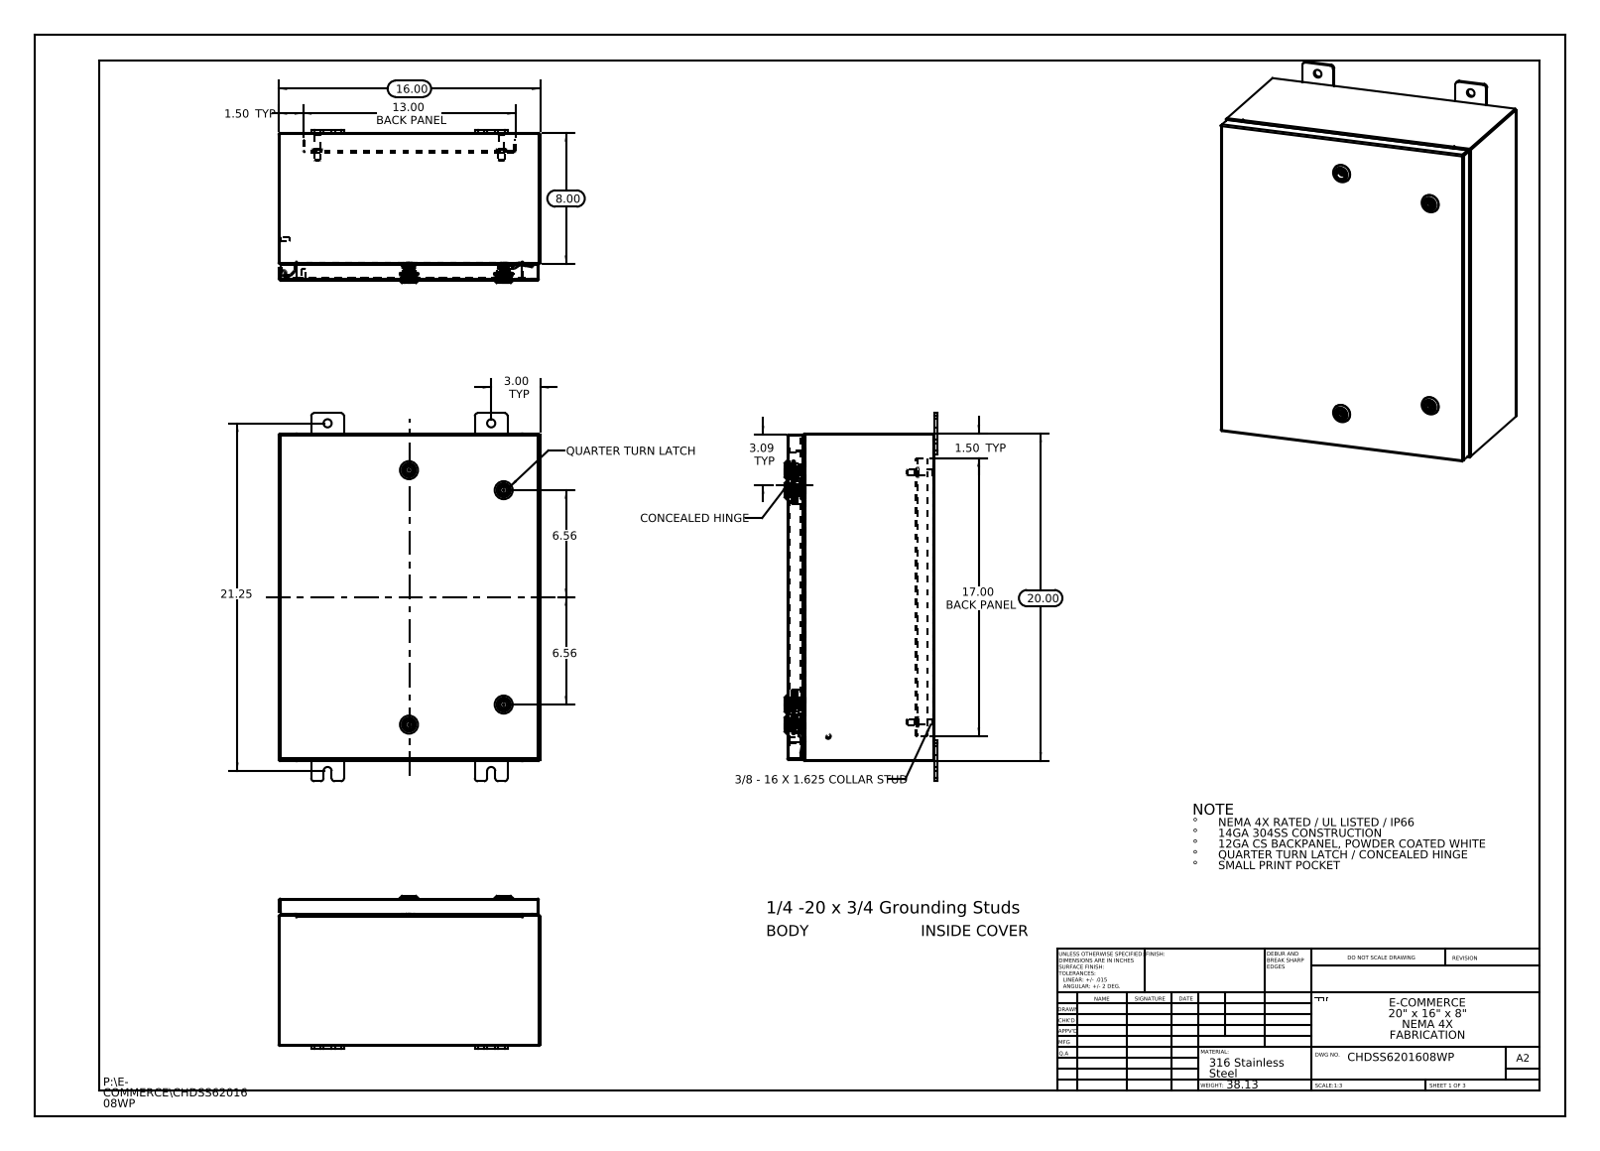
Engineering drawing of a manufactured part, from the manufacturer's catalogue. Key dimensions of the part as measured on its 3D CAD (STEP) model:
Part name (STEP PRODUCT): CHDSS6201608WP Backpanel; Concealed Hinge (Cover Side); Washer-221320-IB-Industrilas_Washer-221320-IB-Industrilas; HW-CLH-E5-8004_Cam-232112-U-Industrilas (+8 more)
STEP written by: SolidWorks 2013 (CONFIG_CONTROL_DESIGN)
Units: inches
Bodies: 43 solids, 3794 faces (1164 planar, 1186 cylindrical, 1444 other)
Overall size (bounding box): 22.5 × 16 × 9.356
Volume: 136.4 in³ · Surface area: 3 426 in²
Round holes (diameter × count): ⌀0.5 ×8, ⌀0.136 ×4, ⌀0.197 ×4, ⌀0.394 ×4, ⌀0.4 ×4, ⌀0.63 ×4, ⌀0.787 ×4, ⌀0.211 ×1
Round bosses / shafts (diameter × count): ⌀0.236 ×6, ⌀1.102 ×4, ⌀0.78 ×4, ⌀0.626 ×4, ⌀0.625 ×4, ⌀0.61 ×4, ⌀0.531 ×4, ⌀0.392 ×4
Partial cylindrical surfaces — rounded edges, fillets, slot ends (radius × count): R0.006 ×132, R0.118 ×132, R0.028 ×48, R0.19 ×24, R0.013 ×20, R0.088 ×18, R0.02 ×16, R0.197 ×16
Main face-to-face distances: 0.075, 0.074, 15.925, 9.01, 8.935, 8.936, 8.861, 19.925, 0.104, 1
Hole centre spacings: 0.688, 1.858, 3.065, 5.916, 10, 11.25, 13.687, 15.25
